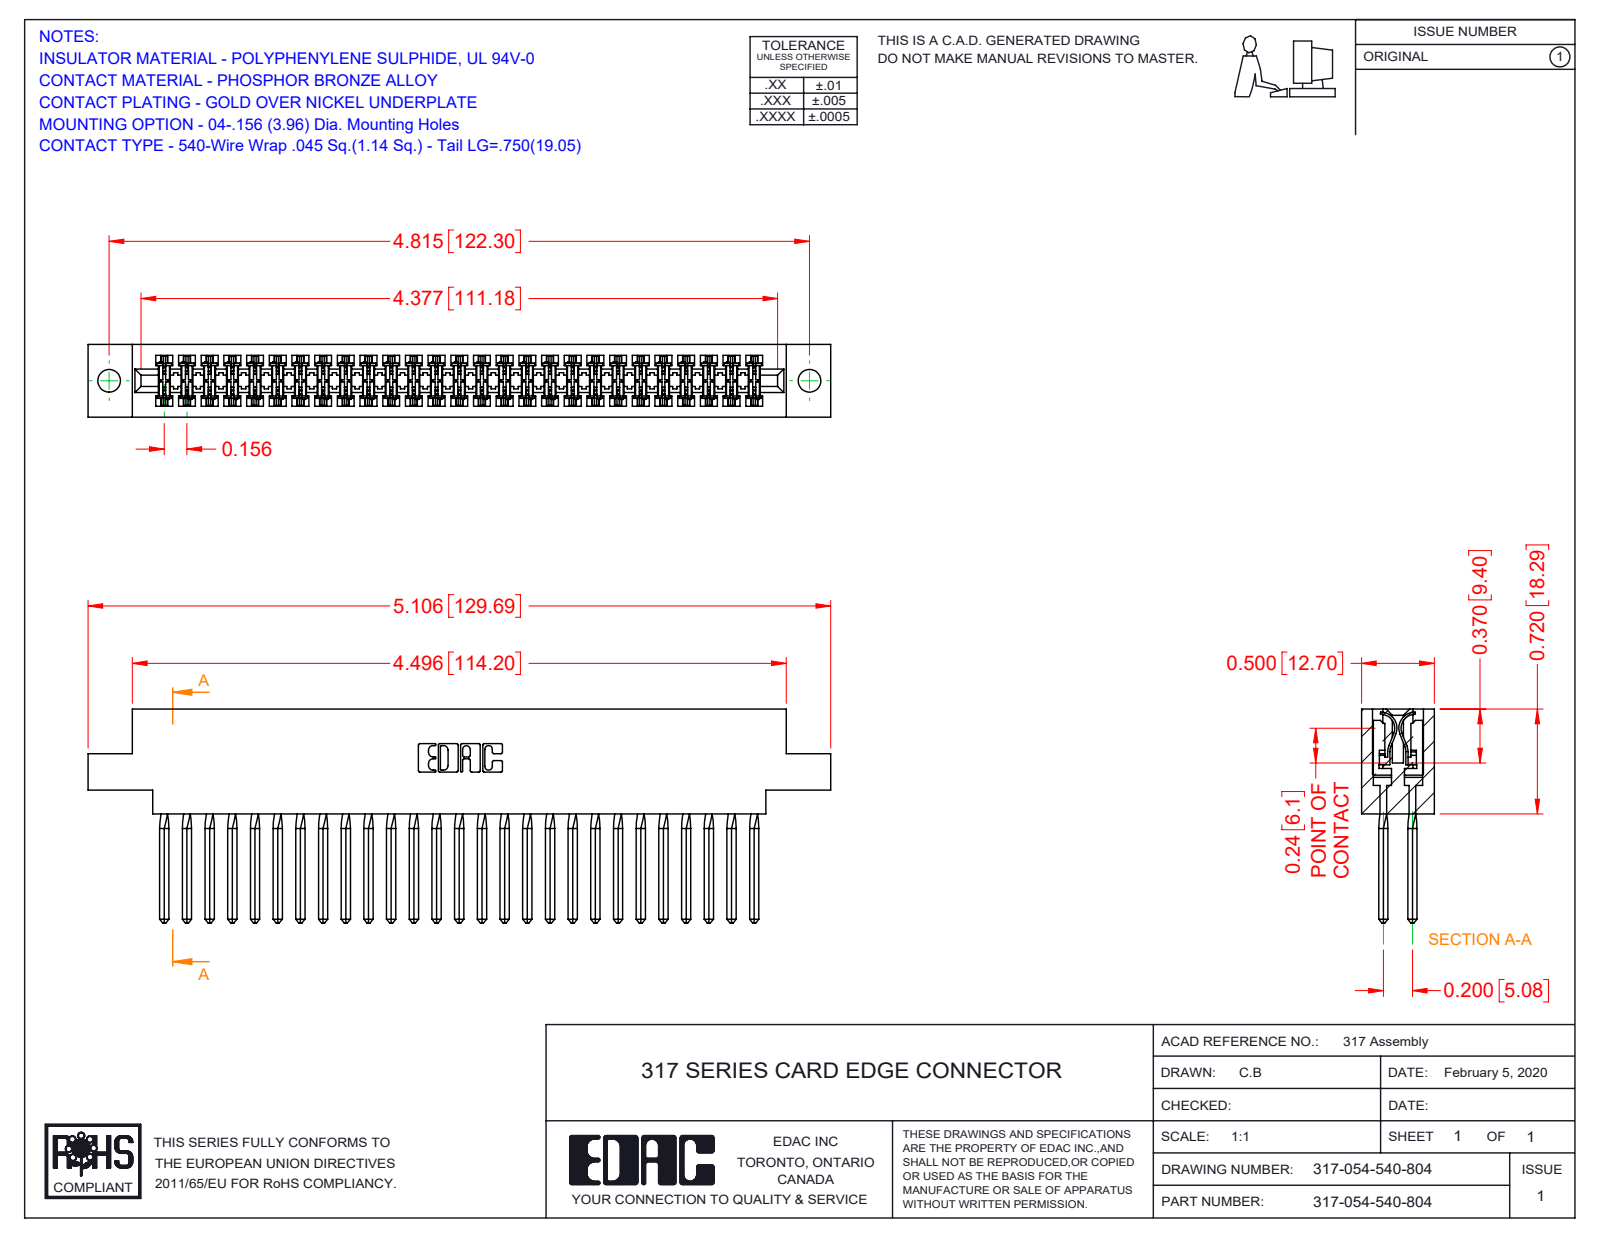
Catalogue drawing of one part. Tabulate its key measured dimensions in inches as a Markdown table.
| quantity | value |
| --- | --- |
| part name | 317 Part_.156 Dia - TH; 317-290-001_540; 317-054-540-804 |
| STEP written by | SolidWorks 2016 (CONFIG_CONTROL_DESIGN) |
| units | inches |
| bodies | 55 solids, 4908 faces (4000 planar, 692 cylindrical, 216 other) |
| overall size | 5.106 × 1.47 × 0.5 |
| volume | 1.292 in³ |
| surface area | 47.78 in² |
| round holes (diameter × count) | 0.156 × 2 |
| partial cylindrical surfaces (radius × count) | 0.015 × 108, 0.01 × 22, 0.007 × 6, 0.031 × 6, 0.026 × 3, 0.095 × 2, 0.1 × 2, 0.11 × 2 |
| main face-to-face distances | 0.5, 0.075, 0.425, 0.35, 0.11, 0.195, 0.094, 0.72, 0.2, 0.115 |
| hole center spacings | 4.815 |
